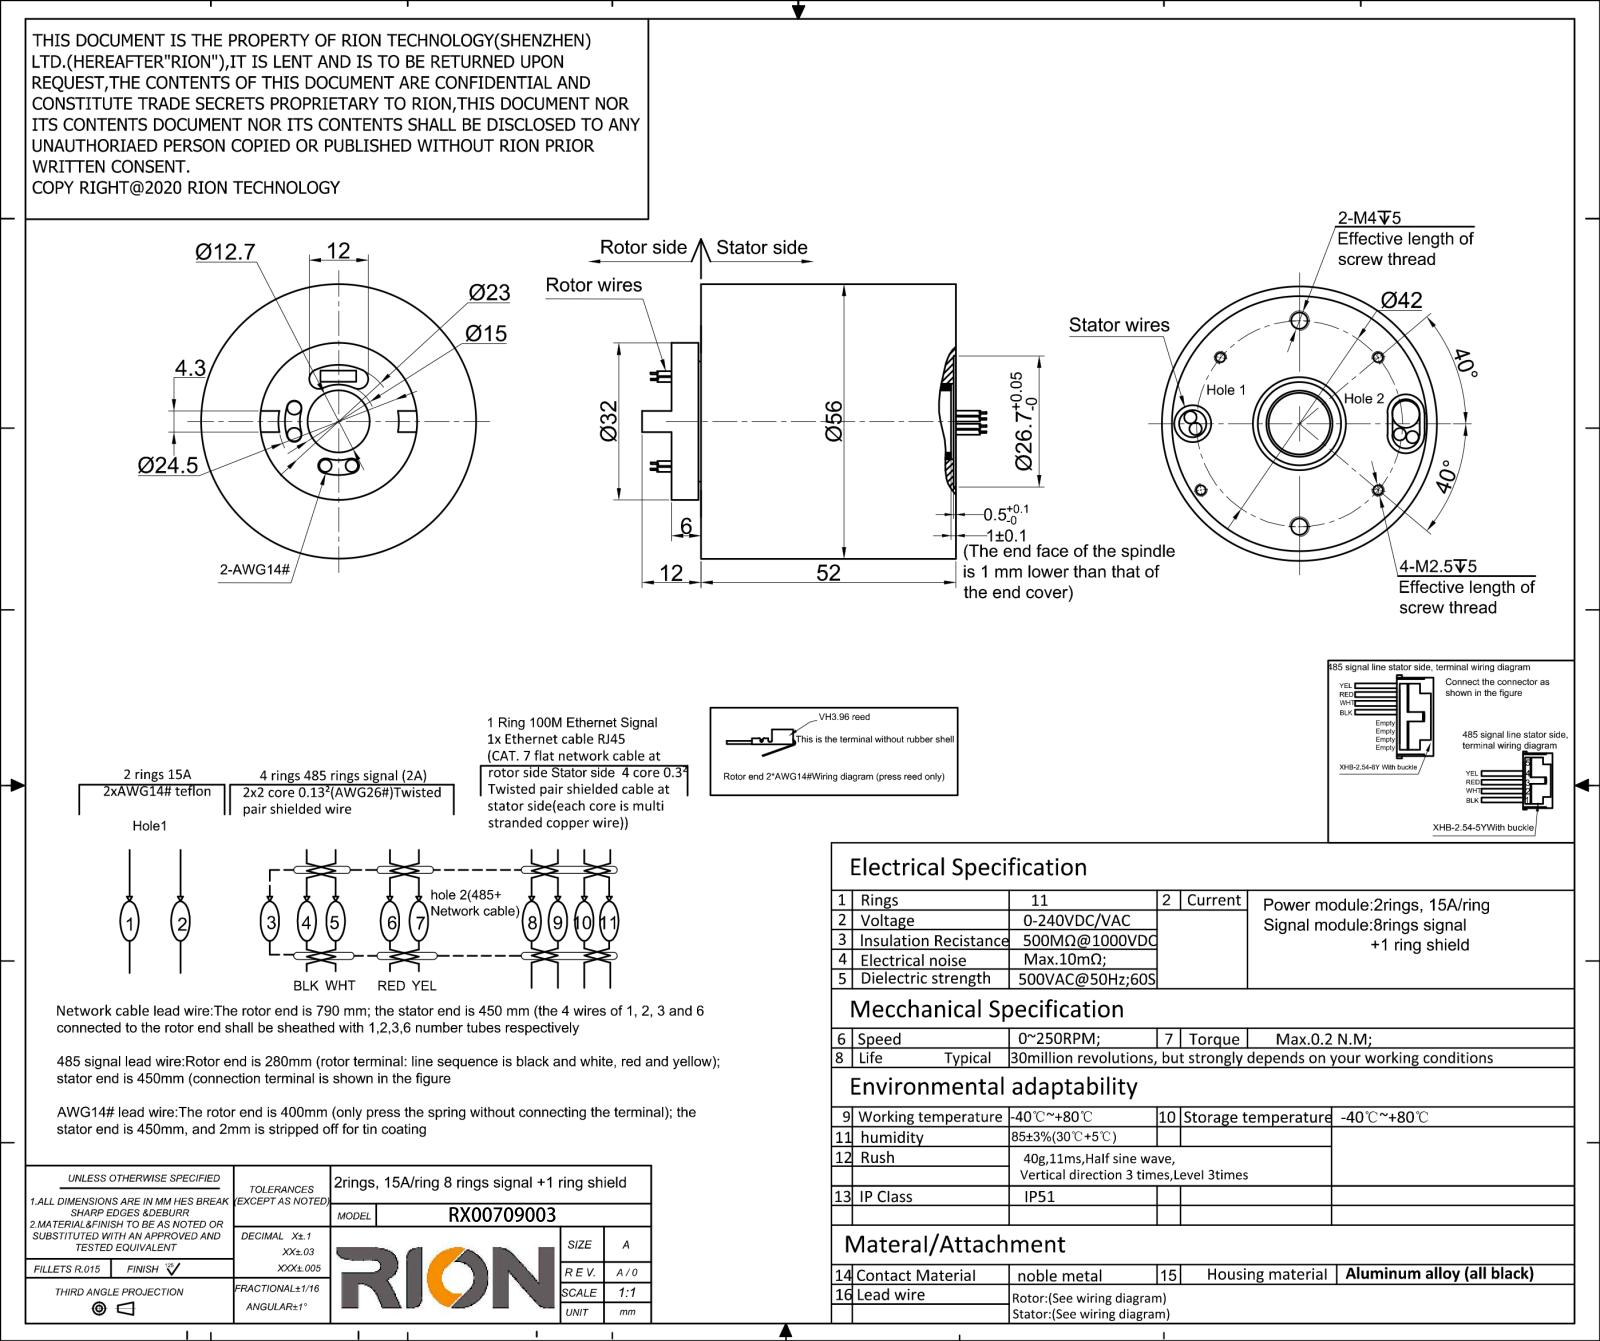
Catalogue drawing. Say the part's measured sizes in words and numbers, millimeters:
The part is named "RT012-P0215-S08-V02". Its 3-D file was written by "SolidWorks 2014 (CONFIG_CONTROL_DESIGN)". It is 1 solid with 128 faces: 48 planar, 80 cylindrical and 0 other. Overall it measures 76.5 by 56 by 56 millimeters. Its volume is 125 811 cubic millimeters and its surface area 20 415 square millimeters. Round holes: 4 of diameter 2.5, 2 of diameter 4, 1 of diameter 5.5, 1 of diameter 12.7, 1 of diameter 15.4, 1 of diameter 15.8, 1 of diameter 26.7, 1 of diameter 53. Round bosses or shafts: 6 of diameter 2.5, 2 of diameter 2.8, 1 of diameter 56, 1 of diameter 52.9, 1 of diameter 52.8, 1 of diameter 32, 1 of diameter 28, 1 of diameter 15.5. Partial cylindrical surfaces (rounded edges, fillets, slot ends): 4 of radius 1.5, 2 of radius 2, 2 of radius 2.75, 1 of radius 7.5, 1 of radius 7.93, 1 of radius 10.93, 1 of radius 11.5, 1 of radius 12.25. The main face-to-face distances are 52, 0.5, 6, 58, 51.5, 57.5, 5.5, 52.5, 57, 51. The hole center spacings are 21, 17.75, 38.07, 14.64, 27, 30.23, 32.18, 40.18.
